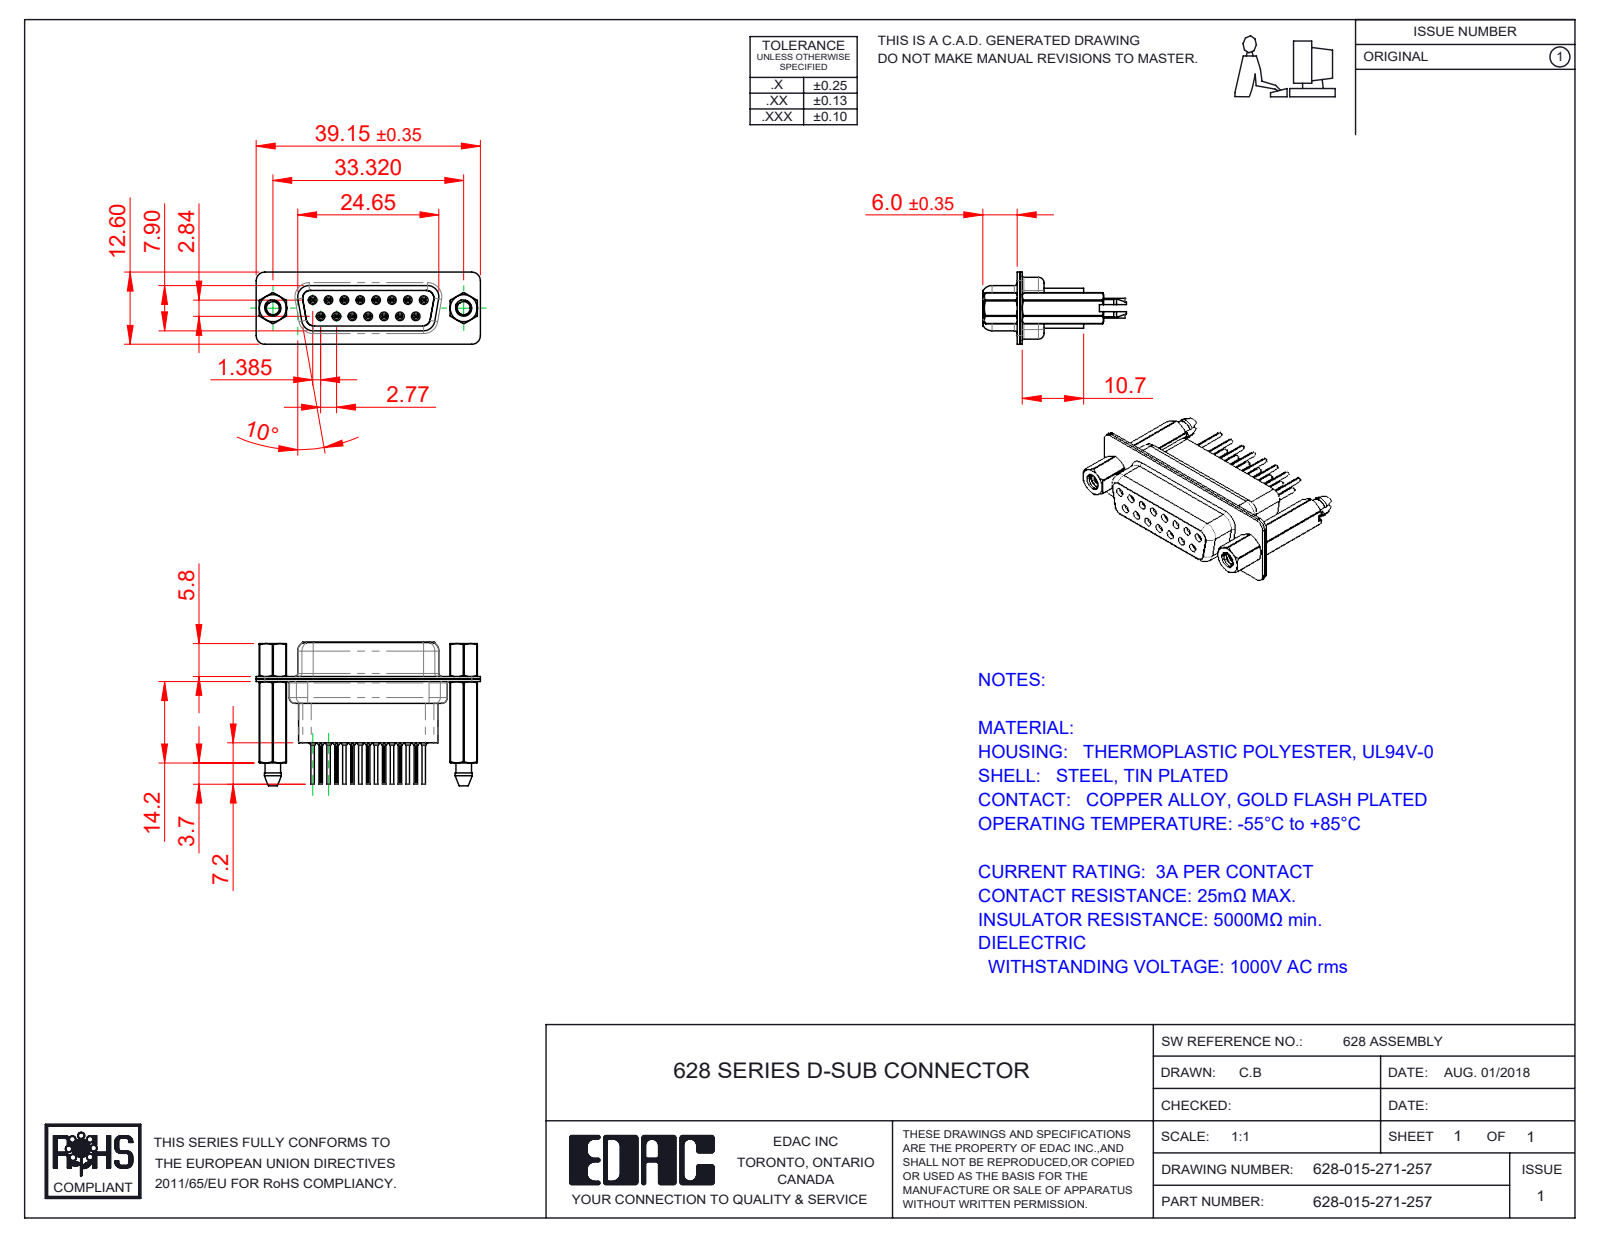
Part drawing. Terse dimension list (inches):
name: 628 Contact Row 1_71; 628 Shell Front_15 Contacts; 628 Housing_15 HP; 628 Shell Rear_15 Contacts (+4 more)
written by: SolidWorks 2020 (CONFIG_CONTROL_DESIGN)
unit: in
bodies: 22 solids, 2324 faces (586 planar, 736 cylindrical, 1002 other)
size: 1.541 × 0.988 × 0.496
volume: 0.236 in³; area: 13.84 in²
holes: 15× ⌀0.008, 15× ⌀0.031, 15× ⌀0.035, 15× ⌀0.043, 15× ⌀0.063, 8× ⌀0.067, 2× ⌀0.089, 2× ⌀0.09, 2× ⌀0.157, 2× ⌀0.159, 2× ⌀0.191
bosses: 15× ⌀0.079, 15× ⌀0.059, 15× ⌀0.047, 15× ⌀0.024, 2× ⌀0.195, 2× ⌀0.189, 2× ⌀0.11
rounds: 30× R0.004, 20× R0.059, 15× R0.011, 12× R0.079, 8× R0.053, 6× R0.063, 4× R0.01, 4× R0.02
face distances: 0.018, 0.016, 0.187, 0.035, 0.26, 0.335, 0.075, 0.276, 0.656, 0.055
hole spacings: 0.124, 0.109, 0.218, 0.327, 0.436, 0.198, 0.198, 0.294
